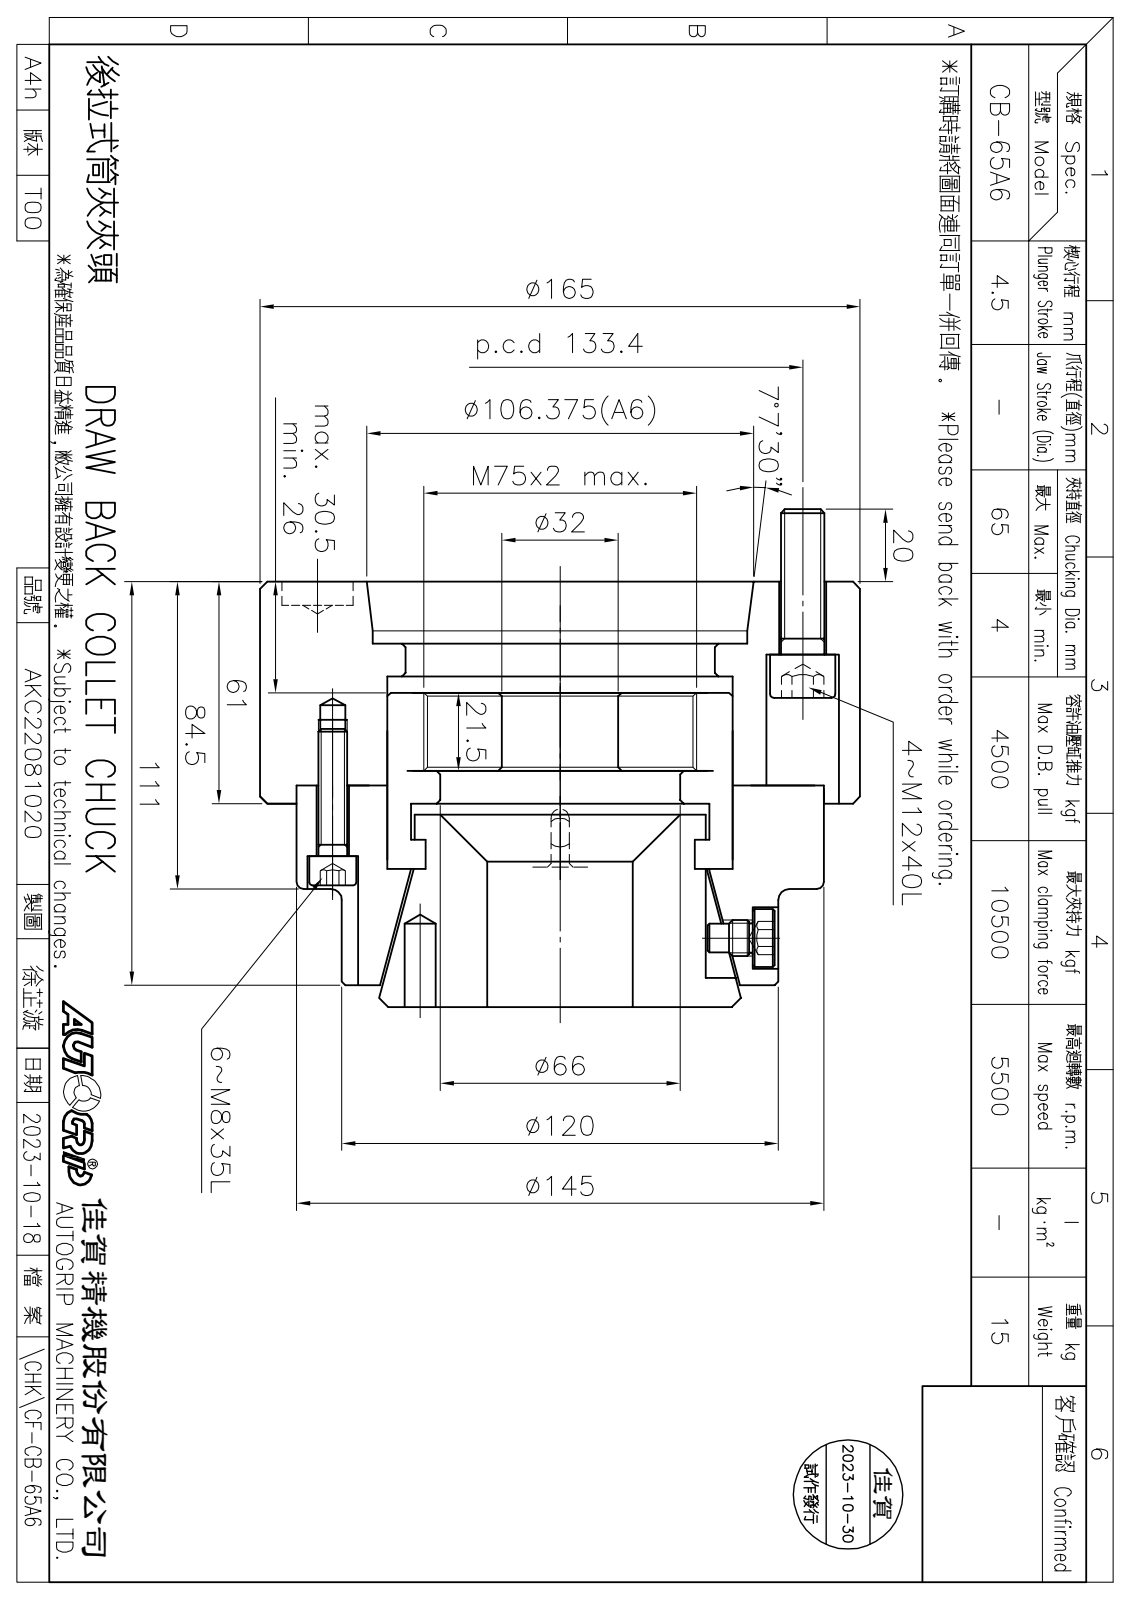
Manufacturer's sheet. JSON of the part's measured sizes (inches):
{"part_name": "圓頭內六角螺栓_M12x40; CF-CB-65A6-01020; 圓頭內六角螺栓_M8x35; CF-CB-65-02010 (+3 more)", "step_written_by": "SolidWorks 2020 (CONFIG_CONTROL_DESIGN)", "units": "inches", "bodies": {"solids": 14, "faces": 496, "planar": 189, "cylindrical": 175, "other": 132}, "overall_size": [6.496, 6.496, 5.394], "volume_in3": 93.31, "surface_area_in2": 408, "round_holes": [[0.268, 6], [0.335, 6], [0.354, 6], [0.551, 6], [0.197, 5], [0.512, 4], [0.787, 4], [0.768, 2], [0.236, 1], [1.575, 1], [2.598, 1], [2.874, 1]], "round_bosses_or_shafts": [[0.512, 6], [0.315, 6], [0.709, 4], [0.472, 4], [6.496, 1], [5.709, 1], [4.724, 1], [4.685, 1]], "face_to_face_distances": [2.205, 2.402, 0.236, 0.925, 1.201, 1.28, 1.516, 0.807, 0.197, 0.118], "hole_center_spacings": [2.461, 2.626, 1.516, 2.626, 4.7, 0.48, 0.678, 0.684]}
